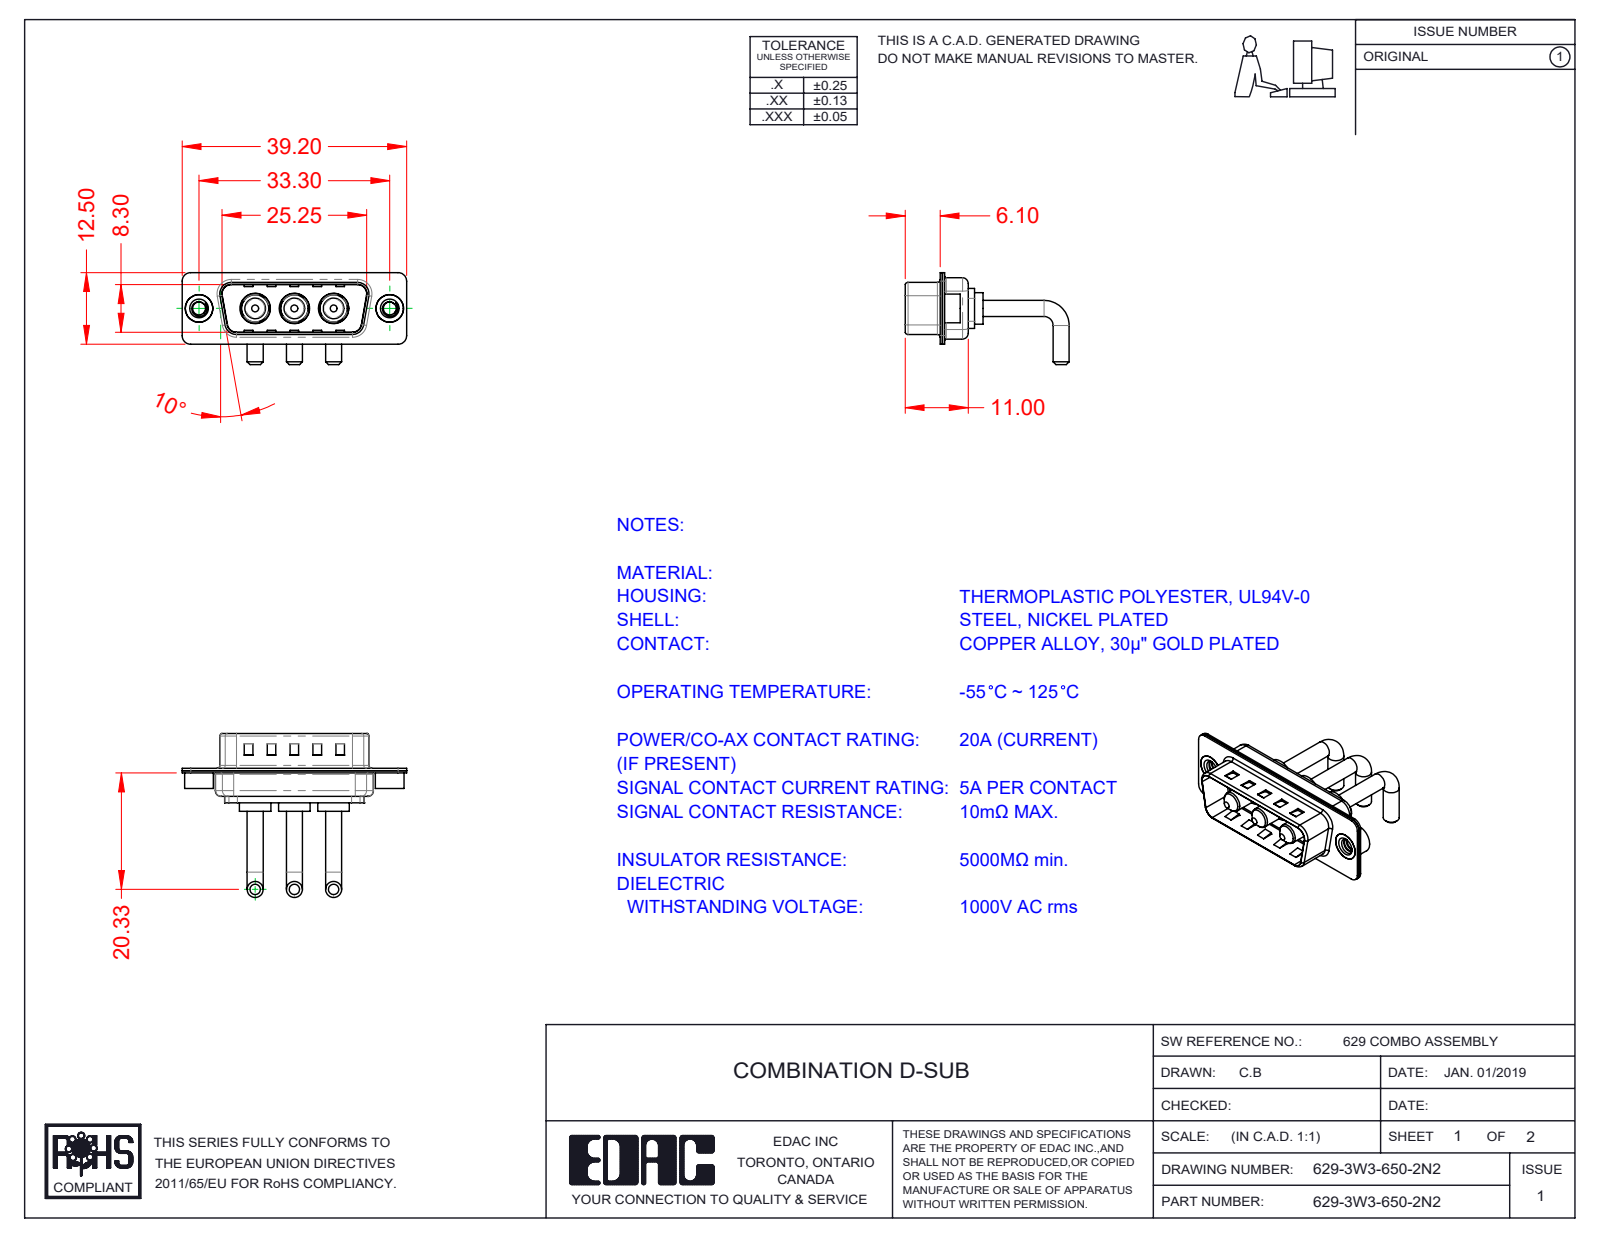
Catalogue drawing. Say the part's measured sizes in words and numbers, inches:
The part is named "629Combo Threaded Rivet_2; 629Combo Shell Front_15 Contacts; Power Pin_Ext 20A RA; 629Combo Housing_3W3 (+2 more)". Its 3-D file was written by "SolidWorks 2020 (CONFIG_CONTROL_DESIGN)". It is 11 solids with 469 faces: 169 planar, 196 cylindrical and 104 other. Overall it measures 1.543 by 1.127 by 0.632 inches. Its volume is 0.145 cubic inches and its surface area 8.026 square inches. Round holes: 3 of diameter 0.191, 3 of diameter 0.209, 2 of diameter 0.089, 2 of diameter 0.157, 2 of diameter 0.189. Round bosses or shafts: 6 of diameter 0.11, 3 of diameter 0.217, 3 of diameter 0.205, 3 of diameter 0.187, 3 of diameter 0.148, 3 of diameter 0.142, 2 of diameter 0.197, 2 of diameter 0.193. Partial cylindrical surfaces (rounded edges, fillets, slot ends): 16 of radius 0.059, 12 of radius 0.079, 8 of radius 0.02, 8 of radius 0.063, 4 of radius 0.01, 4 of radius 0.024, 4 of radius 0.026, 4 of radius 0.035. The main face-to-face distances are 0.016, 0.031, 0.374, 0.358, 0.343, 0.39, 0.03, 0.047, 0.014, 0.236. The hole center spacings are 0.27, 0.386, 0.656, 0.925, 0.539, 1.311.
